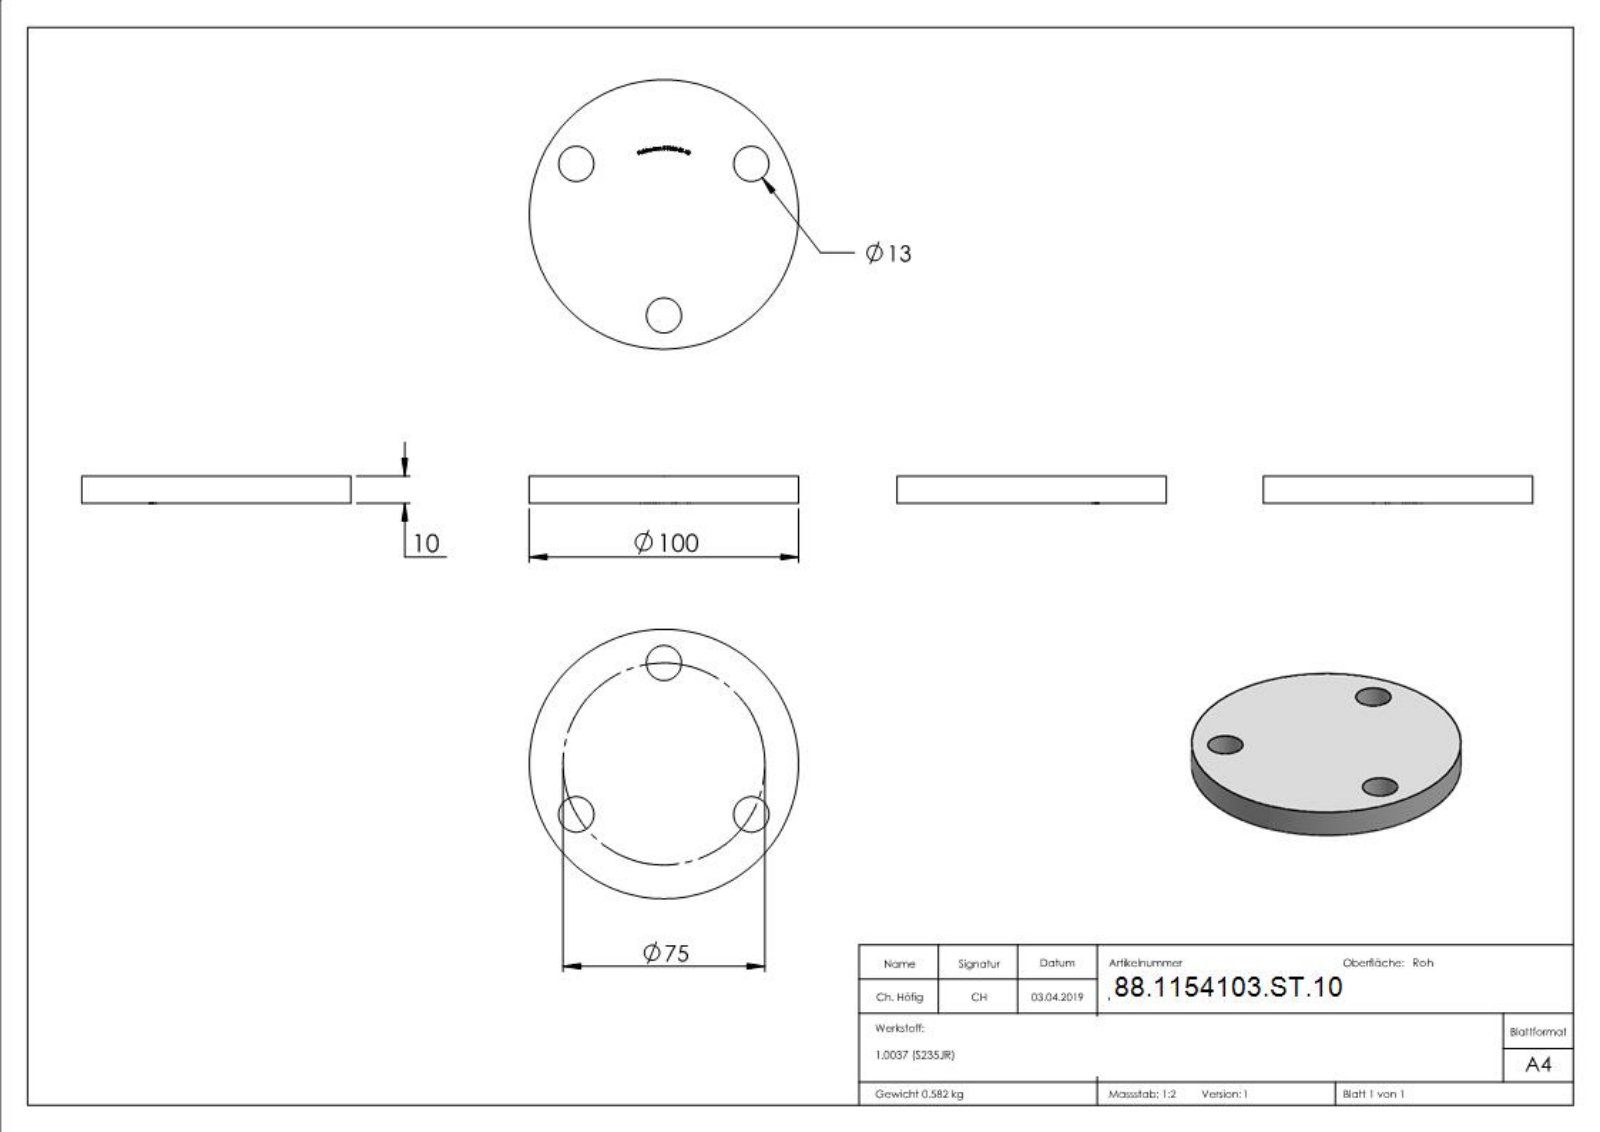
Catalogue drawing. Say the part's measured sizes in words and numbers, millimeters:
The part is named "54103-ST-10". Its 3-D file was written by "SolidWorks 2015 (CONFIG_CONTROL_DESIGN)". It is 1 solid with 244 faces: 133 planar, 8 cylindrical and 103 other. Overall it measures 100 by 100 by 10 millimeters. Its volume is 74 557 cubic millimeters and its surface area 19 288 square millimeters. Round holes: 3 of diameter 13. Round bosses or shafts: 1 of diameter 100. The main face-to-face distances are 10, 9.9, 0.72, 0.54, 0.67, 0.6, 0.66, 1.33, 1.46, 0.41. The hole center spacings are 64.95, 64.96.
